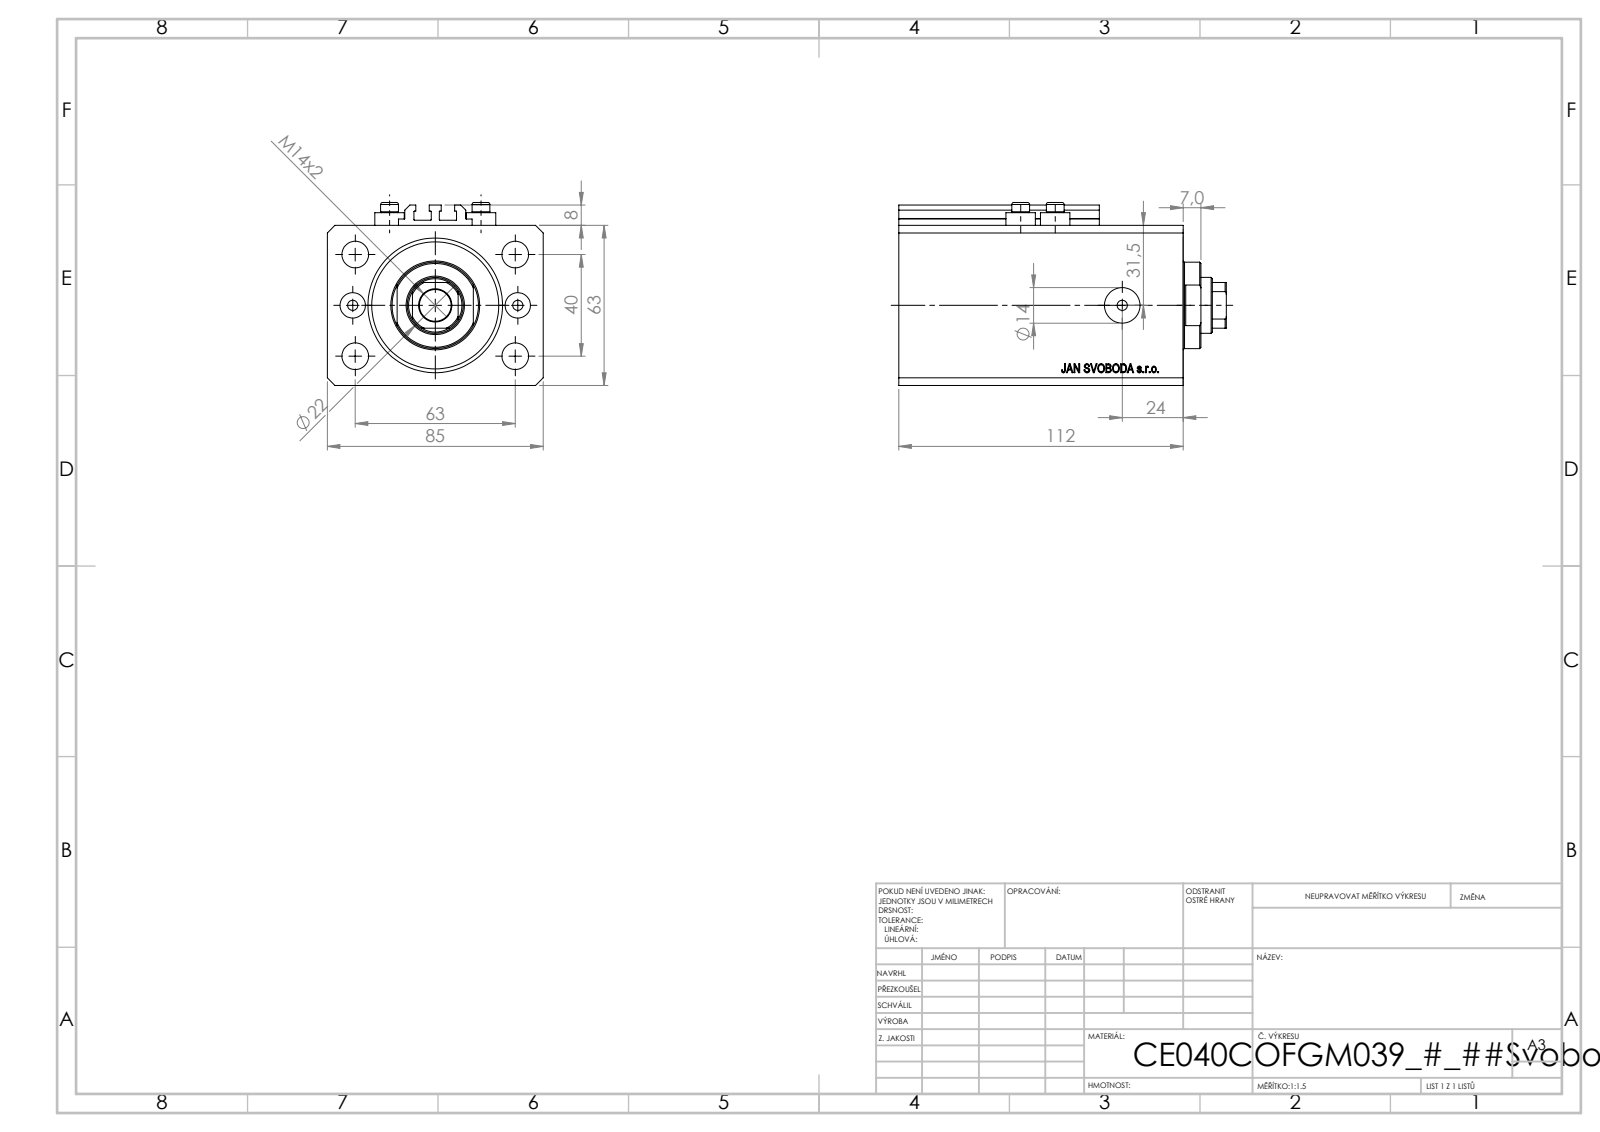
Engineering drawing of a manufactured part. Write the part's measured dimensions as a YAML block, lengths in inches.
part_name: "V250CE_VC_C; V250CE_C_Body; ALLEN BOLT V250CE; V250CE_C_VCP"
step_written_by: "SolidWorks 2019 (CONFIG_CONTROL_DESIGN)"
units: inches
bodies: {solids: 8, faces: 1034, planar: 504, cylindrical: 86, other: 444}
overall_size: [5.079, 3.346, 2.835]
volume: 33
surface_area: 164
round_holes:
  - {diameter: 0.157, count: 8}
  - {diameter: 0.413, count: 4}
  - {diameter: 0.394, count: 2}
  - {diameter: 0.551, count: 2}
  - {diameter: 0.492, count: 1}
  - {diameter: 0.866, count: 1}
  - {diameter: 1.575, count: 1}
  - {diameter: 2.087, count: 1}
round_bosses_or_shafts:
  - {diameter: 0.457, count: 4}
  - {diameter: 0.276, count: 4}
  - {diameter: 1.339, count: 1}
partial_cylinders:
  - {radius: 0.008, count: 10}
  - {radius: 0.413, count: 1}
face_to_face_distances: [2.48, 3.346, 4.409, 0.669, 3.74, 0.449, 3.291, 3.961, 2.205, 0.118]
hole_center_spacings: [0.788, 1.469, 2.64, 0.535, 1.28, 1.417, 1.515, 1.575]
